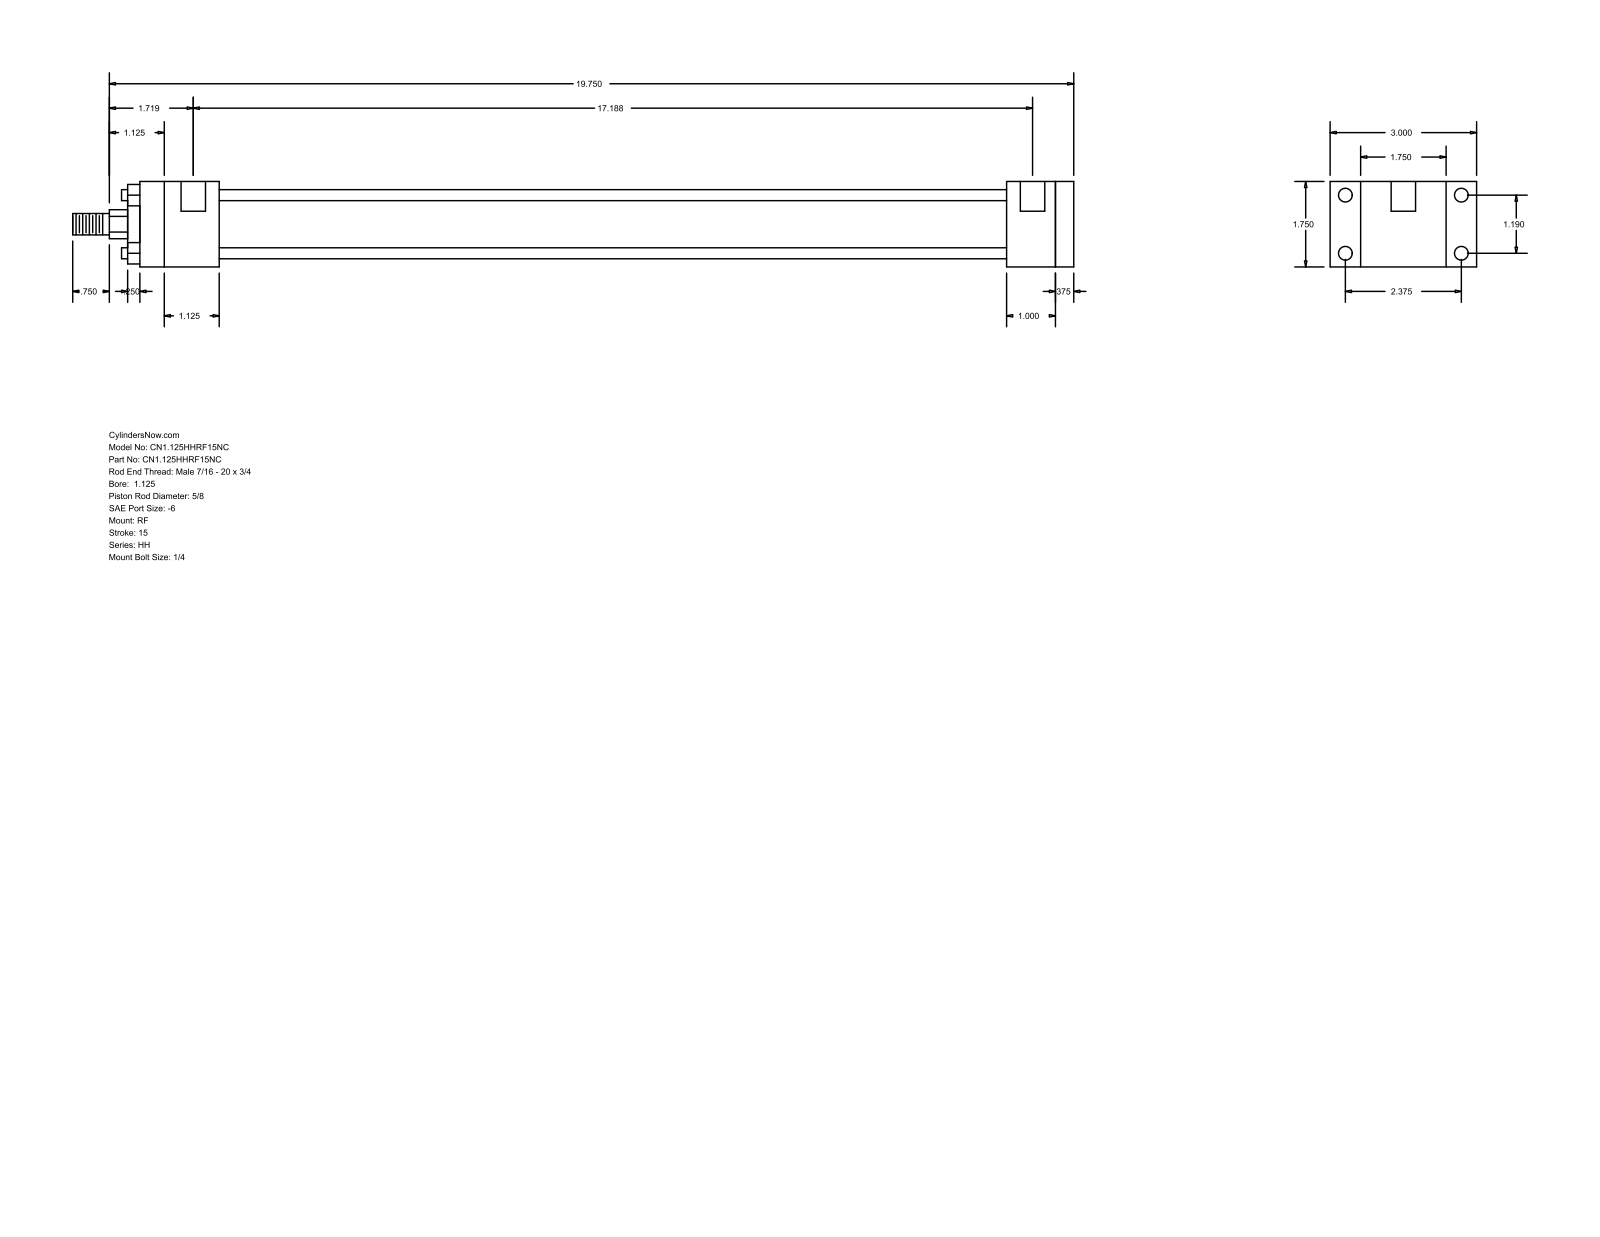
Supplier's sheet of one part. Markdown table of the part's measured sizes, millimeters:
| quantity | value |
| --- | --- |
| part name | HH_RF__0112_0.625 |
| STEP written by | GSSL Pune (CONFIG_CONTROL_DESIGN) |
| units | millimeters |
| bodies | 0 solids, 92 faces (64 planar, 28 cylindrical, 0 other) |
| overall size | 520.7 × 76.2 × 44.45 |
| round holes (diameter × count) | 5.56 × 4, 7.14 × 4, 12.7 × 2 |
| round bosses / shafts (diameter × count) | 5.71 × 4, 34.92 × 1, 28.57 × 1, 15.88 × 1, 11.11 × 1 |
| partial cylindrical surfaces (radius × count) | 7.54 × 1 |
| main face-to-face distances | 44.46, 9.53, 485.77, 15.87, 434.97, 444.5, 409.58, 25.39, 34.92, 41.27 |
| hole center spacings | 30.22, 60.32, 67.47, 433.39, 3.17, 436.56 |
